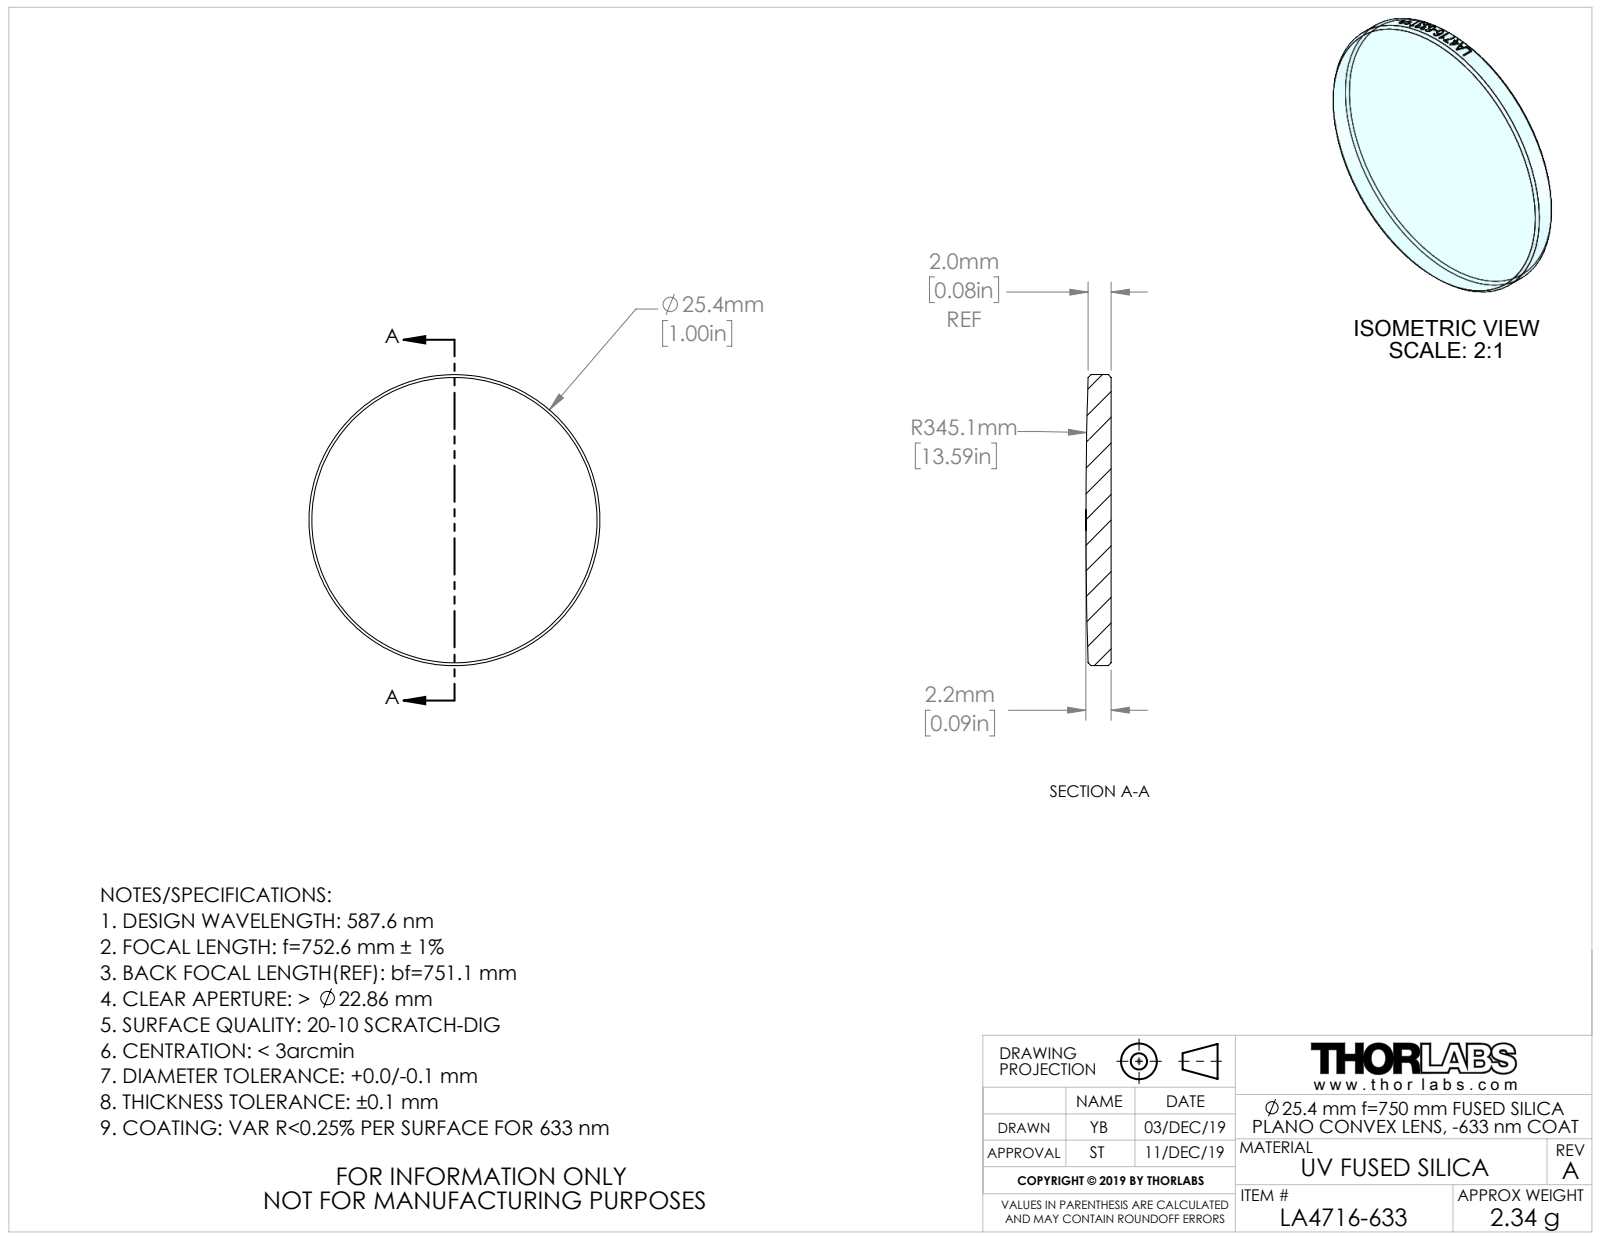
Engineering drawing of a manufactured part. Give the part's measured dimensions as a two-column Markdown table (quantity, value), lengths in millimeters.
| quantity | value |
| --- | --- |
| part name | CTN015172; CTN015171-999 |
| STEP written by | SolidWorks 2018 (AUTOMOTIVE_DESIGN) |
| units | millimeters |
| bodies | 1 solid, 27 faces (1 planar, 20 cylindrical, 6 other) |
| overall size | 25.4 × 25.4 × 2.2 |
| volume | 1 062 mm³ |
| surface area | 1 150 mm² |
| round bosses / shafts (diameter × count) | 25.4 × 1 |
